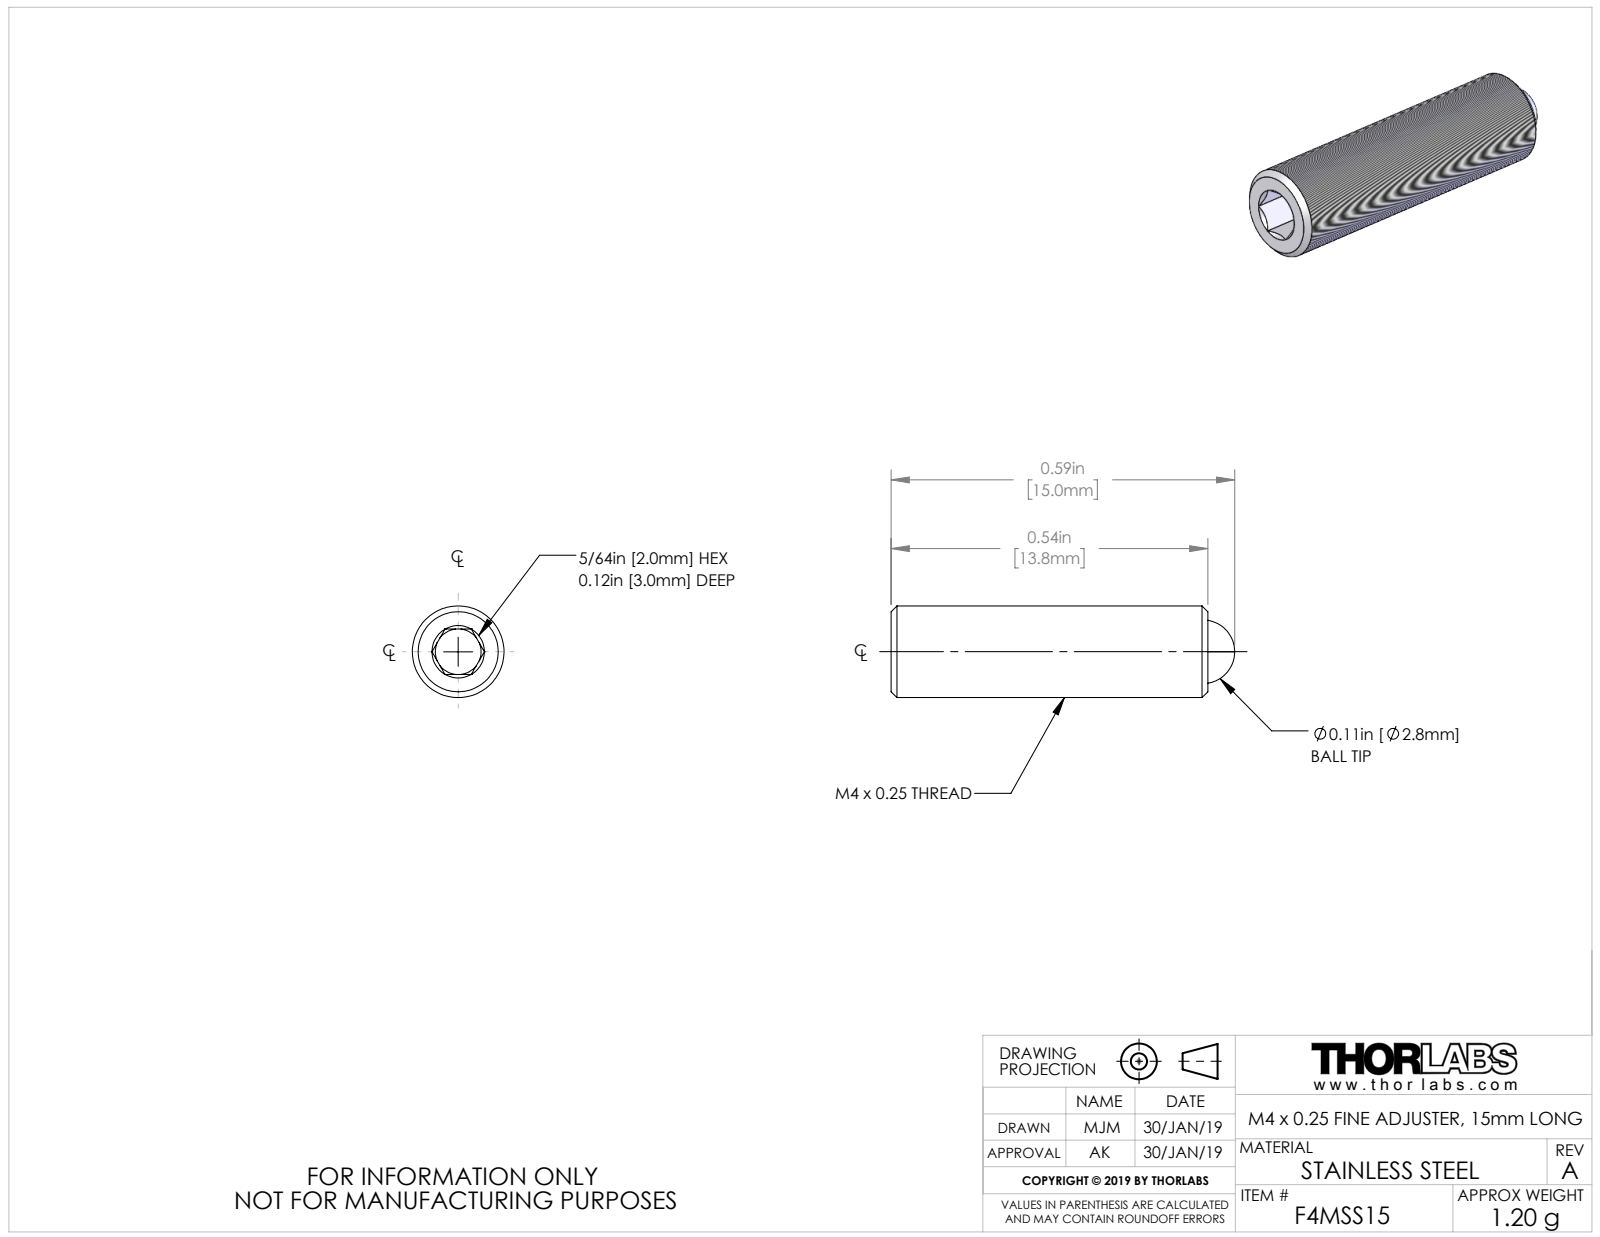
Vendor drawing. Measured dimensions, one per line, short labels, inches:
name: TTN174701-E0W
written by: SolidWorks 2018 (AUTOMOTIVE_DESIGN)
unit: in
bodies: 2 solids, 45 faces (20 planar, 6 cylindrical, 19 other)
size: 0.591 × 0.157 × 0.157
volume: 0.01 in³; area: 0.396 in²
holes: 1× ⌀0.079, 1× ⌀0.11
bosses: 1× ⌀0.157
face distances: 0.078, 0.545, 0.425, 0.12
